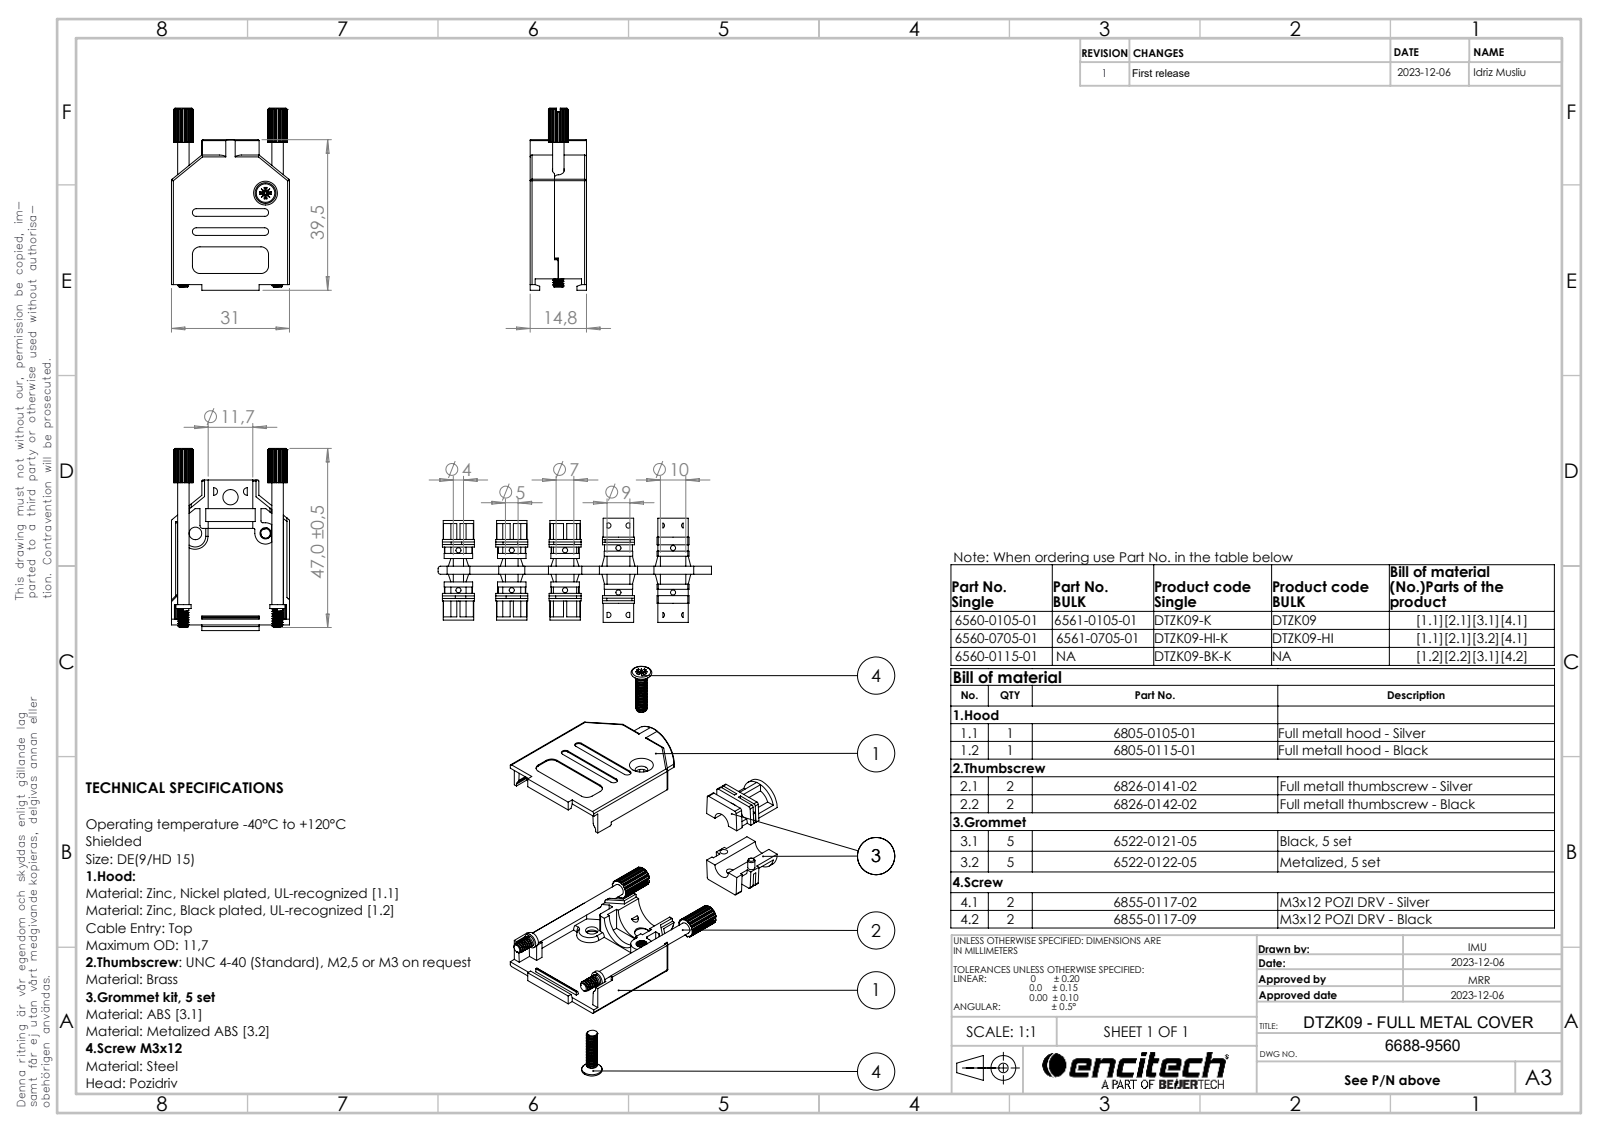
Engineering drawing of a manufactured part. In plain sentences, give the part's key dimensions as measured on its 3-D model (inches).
The part is named "6688-9560; 6805-0105-01; 6826-0141-02; 6855-0117-02 (+1 more)". Its 3-D file was written by "SolidWorks 2021 (AUTOMOTIVE_DESIGN)". It is 8 solids with 870 faces: 432 planar, 352 cylindrical and 86 other. Overall it measures 1.882 by 1.22 by 0.583 inches. Its volume is 0.431 cubic inches and its surface area 17.04 square inches. Round holes: 3 of diameter 0.079, 2 of diameter 0.098, 2 of diameter 0.122, 2 of diameter 0.13, 1 of diameter 0.157, 1 of diameter 0.197, 1 of diameter 0.461. Round bosses or shafts: 2 of diameter 0.157, 2 of diameter 0.118, 2 of diameter 0.114, 2 of diameter 0.112, 2 of diameter 0.075, 1 of diameter 0.591, 1 of diameter 0.441. Partial cylindrical surfaces (rounded edges, fillets, slot ends): 26 of radius 0.02, 12 of radius 0.039, 10 of radius 0.01, 8 of radius 0.004, 6 of radius 0.008, 4 of radius 0.079, 4 of radius 0.233, 2 of radius 0.012. The main face-to-face distances are 0.051, 0.531, 0.291, 0.24, 0.583, 0.48, 0.039, 0.063, 0.28, 0.571. The hole center spacings are 0.227, 0.252, 0.27, 0.372, 0.486, 0.52, 0.595, 0.287.
